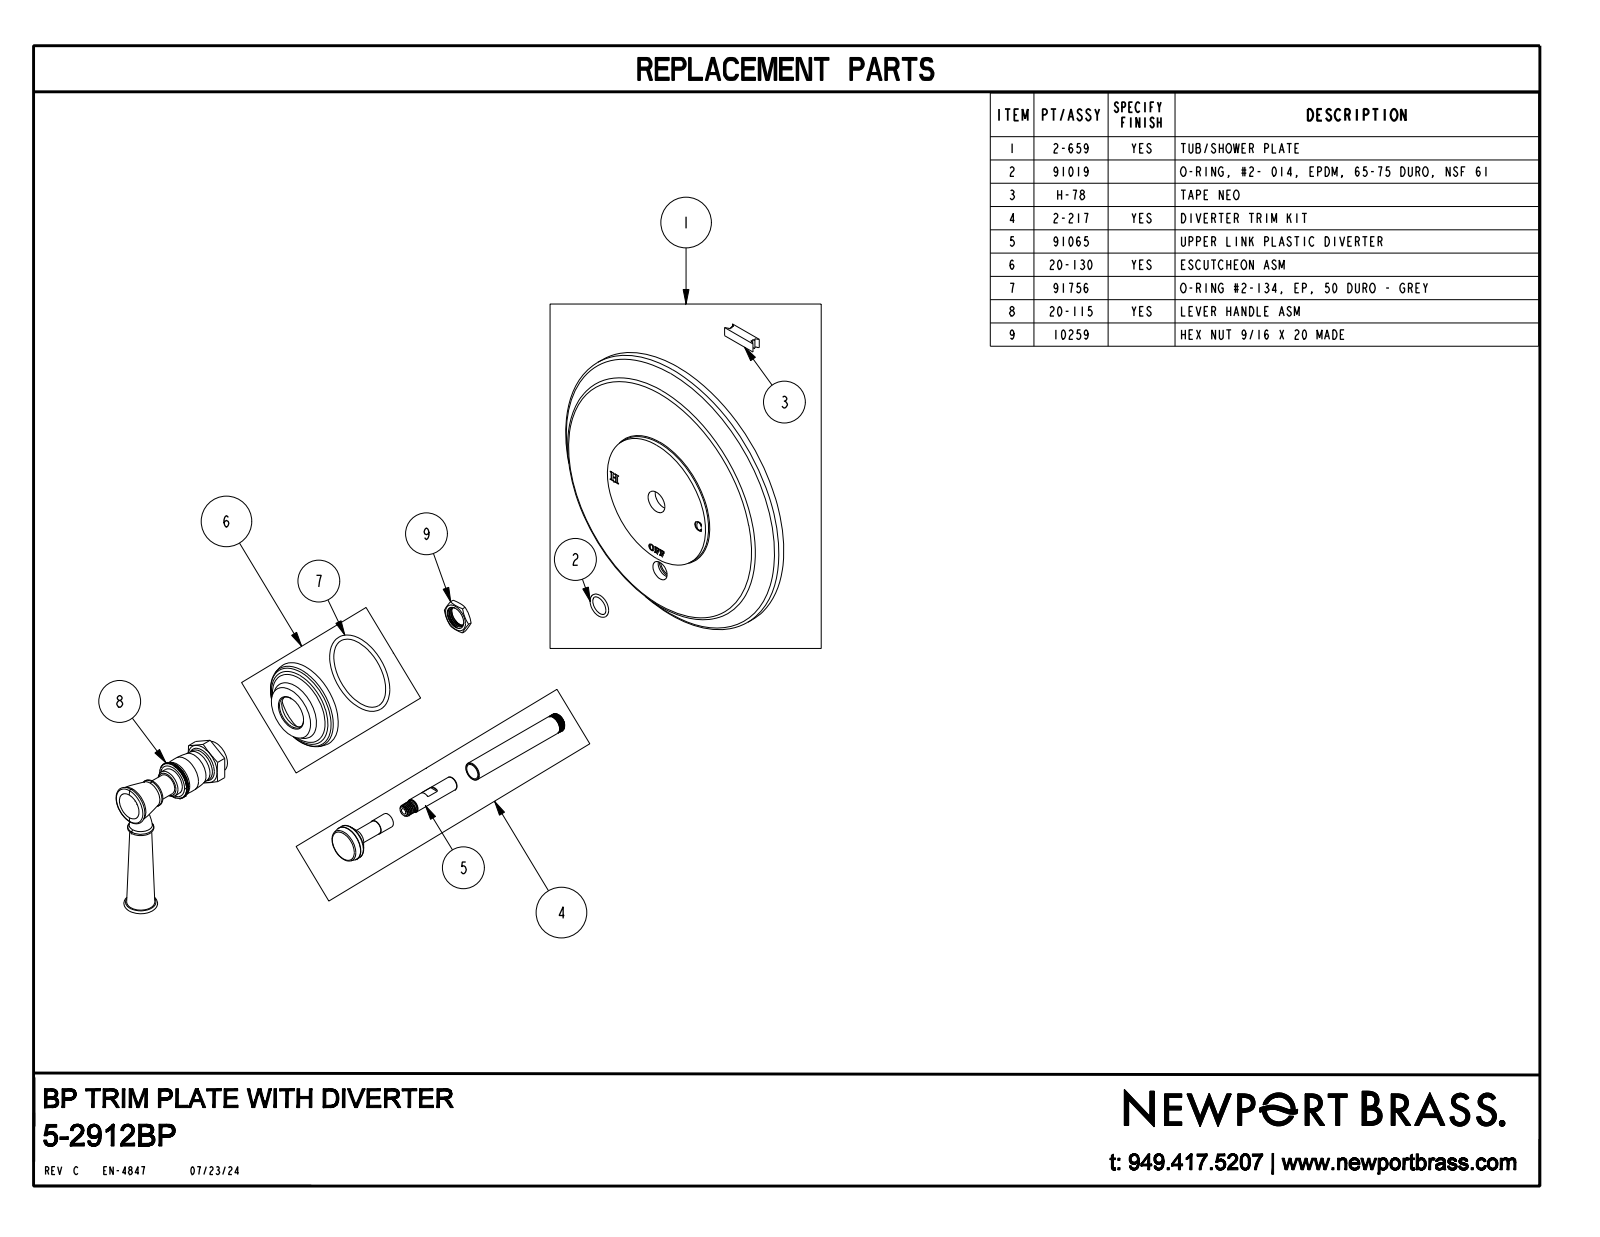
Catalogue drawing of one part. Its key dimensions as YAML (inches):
part_name: "5-2912BP"
step_written_by: "CREO PARAMETRIC BY PTC INC, 2018400 (CONFIG_CONTROL_DESIGN)"
units: inches
bodies: {solids: 1, faces: 513, planar: 230, cylindrical: 12, other: 271}
overall_size: [7.5, 7.5, 4.169]
volume: 30.05
surface_area: 117.3
round_bosses_or_shafts:
  - {diameter: 7.5, count: 1}
  - {diameter: 0.9, count: 1}
  - {diameter: 0.686, count: 1}
  - {diameter: 0.53, count: 1}
  - {diameter: 0.472, count: 1}
  - {diameter: 0.354, count: 1}
face_to_face_distances: [0.625, 0.75, 0.125, 1.284, 0.659, 0.534, 1.977, 1.352, 1.227, 0.693]
